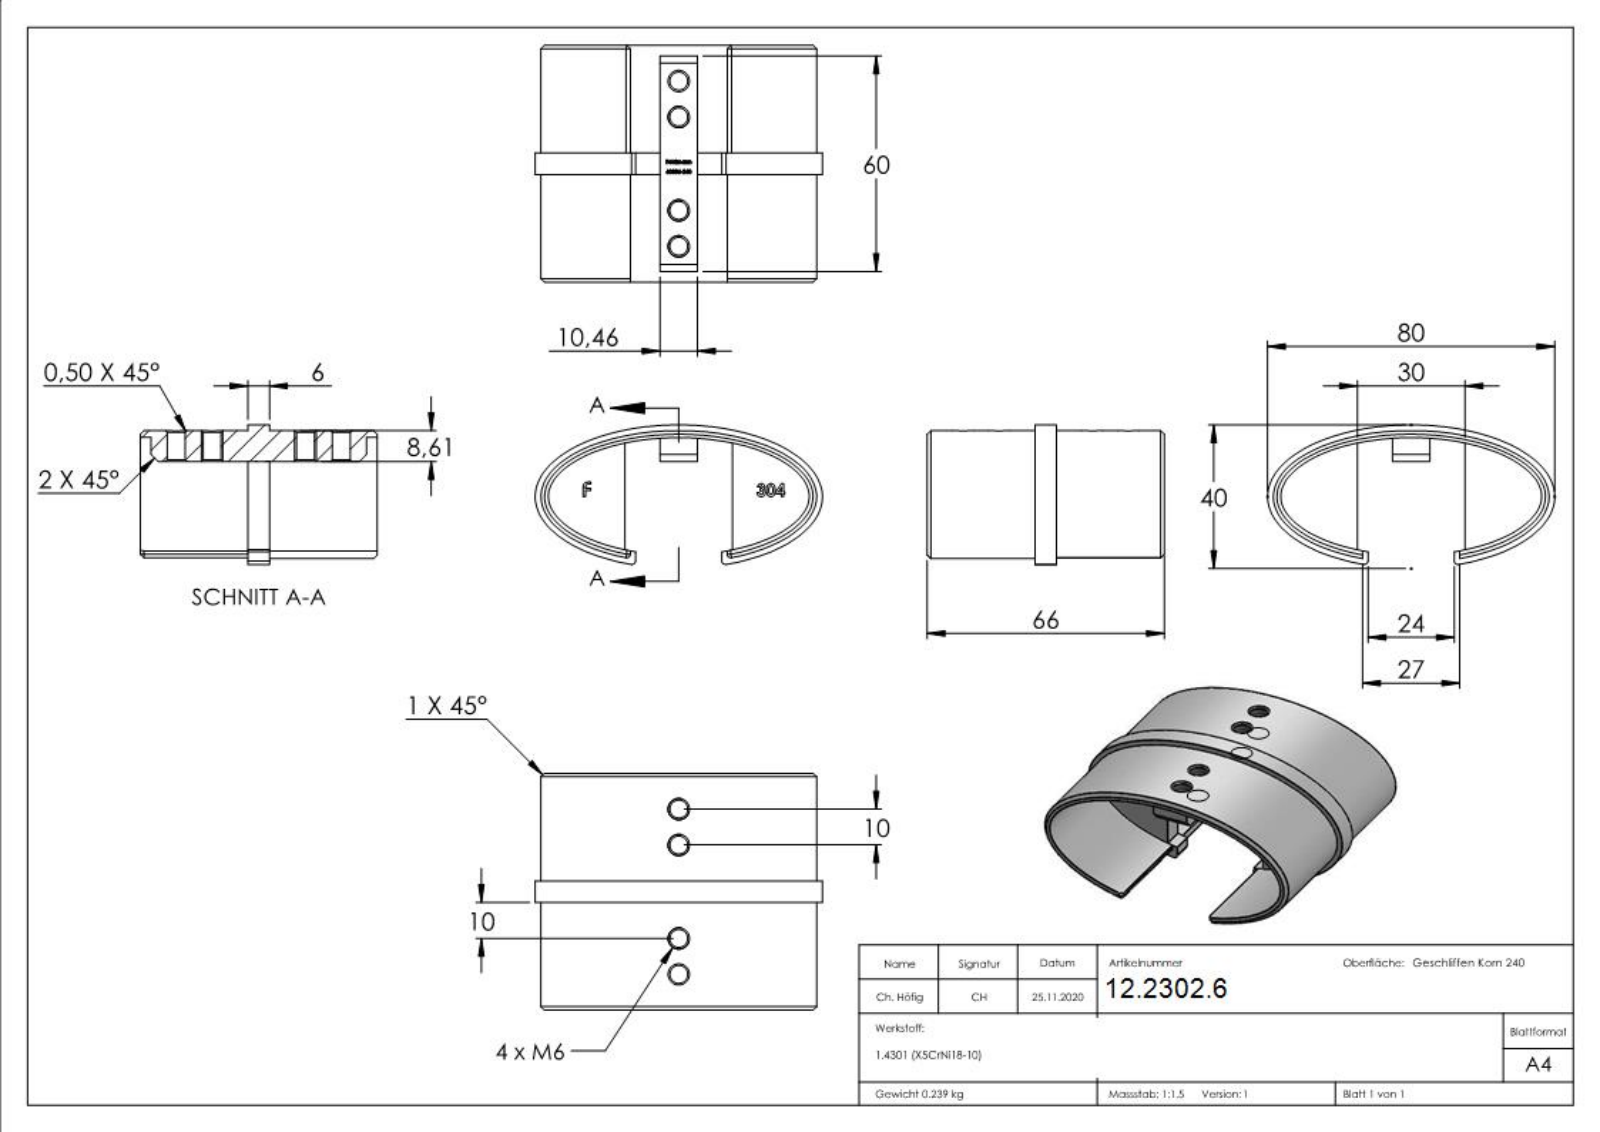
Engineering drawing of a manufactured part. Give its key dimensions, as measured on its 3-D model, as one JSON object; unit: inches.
{"part_name": "60336-240", "step_written_by": "SolidWorks 2018 (CONFIG_CONTROL_DESIGN)", "units": "inches", "bodies": {"solids": 1, "faces": 362, "planar": 172, "cylindrical": 12, "other": 178}, "overall_size": [3.15, 2.598, 1.531], "volume_in3": 1.878, "surface_area_in2": 37.05, "round_holes": [[0.197, 4]], "partial_cylinders_radius": [[0.039, 4]], "face_to_face_distances": [0.236, 1.181, 0.412, 0.385, 0.796, 1.417, 1.063, 0.059, 1.122, 0.326], "hole_center_spacings": [0.394, 1.417, 1.024, 1.811]}
